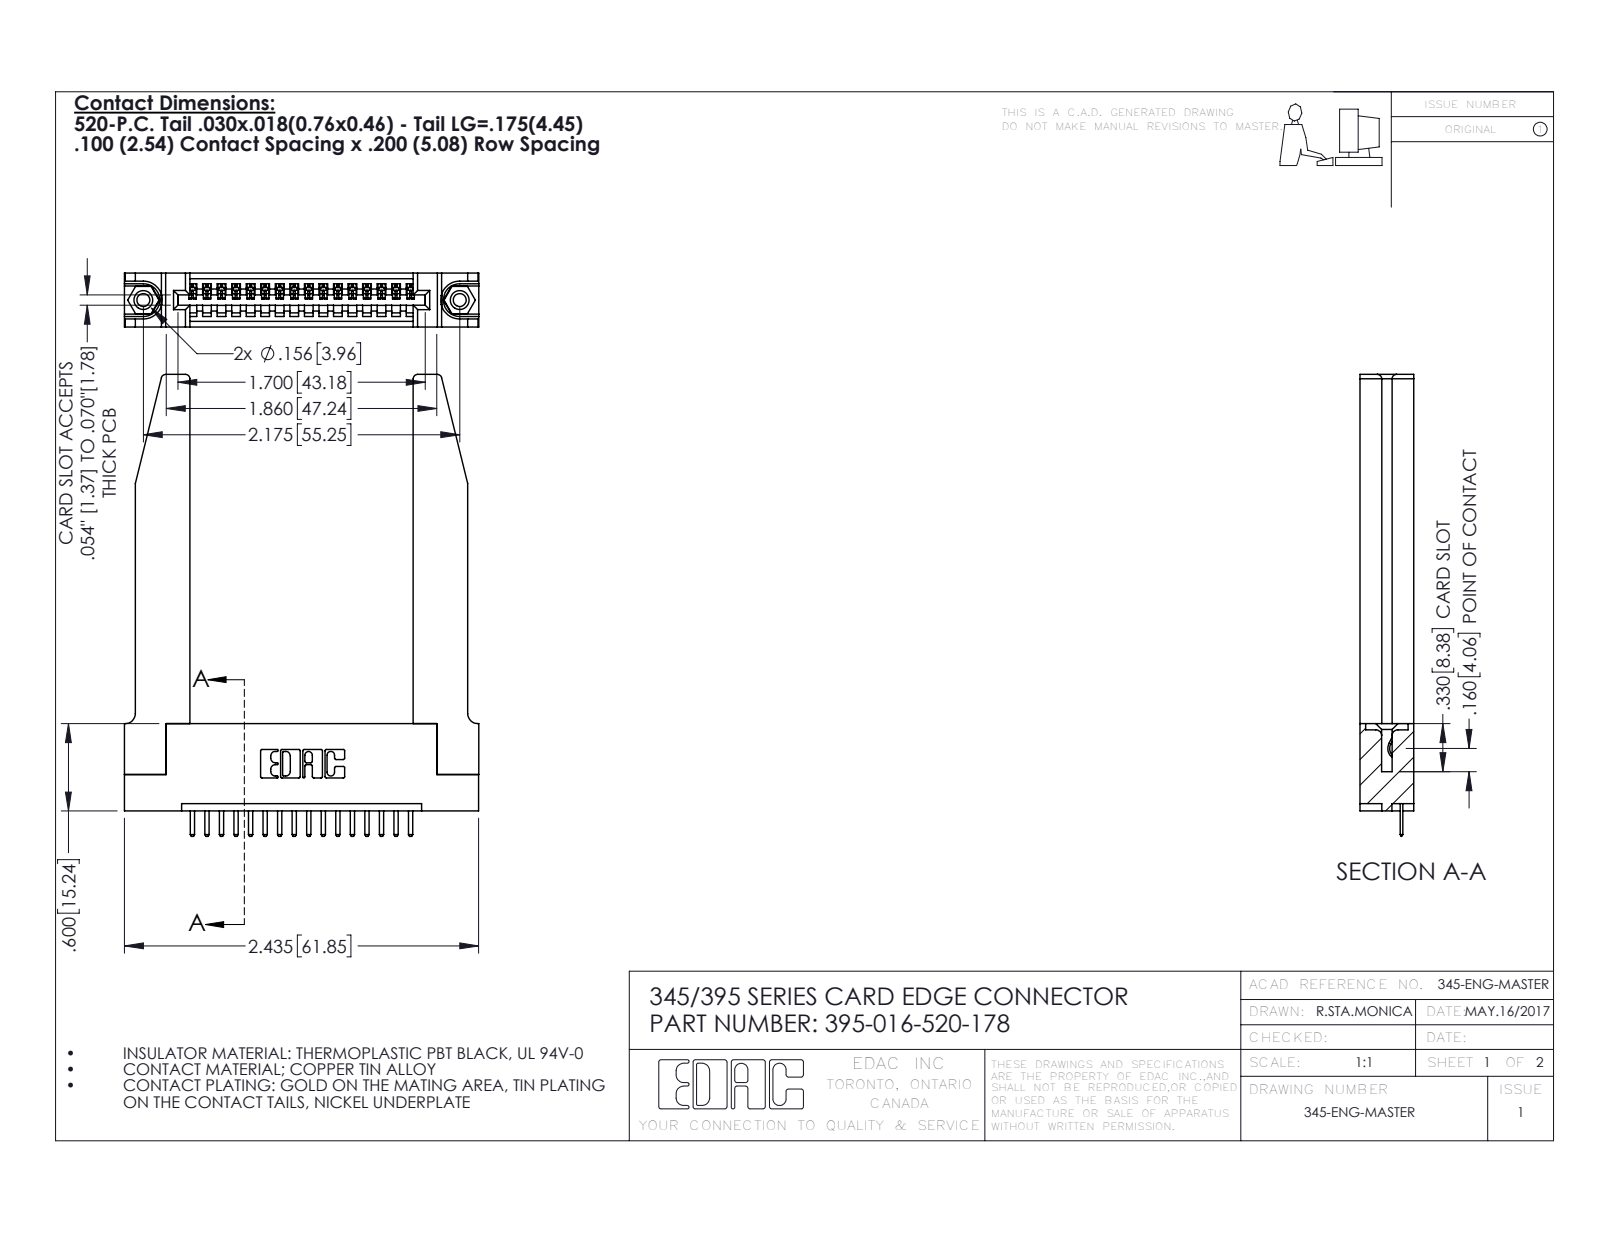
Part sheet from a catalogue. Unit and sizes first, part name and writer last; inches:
Units: inches
Overall size (bounding box): 3.175 × 2.436 × 0.37
Round holes (diameter × count): ⌀0.089 ×2, ⌀0.125 ×2, ⌀0.156 ×2, ⌀0.064 ×1
Round bosses / shafts (diameter × count): ⌀0.155 ×2
Partial cylindrical surfaces — rounded edges, fillets, slot ends (radius × count): R0.01 ×34, R0.006 ×32, R0.01 ×22, R0.03 ×8, R0.007 ×6, R0.031 ×6, R0.026 ×3, R0.031 ×2
Main face-to-face distances: 0.37, 0.072, 0.298, 0.2, 0.148, 0.15, 0.077, 0.22, 1.535, 0.098
Hole centre spacings: 0.27, 1.942, 2.175
Volume: 0.817 in³ · Surface area: 21.4 in²
Bodies: 21 solids, 1352 faces (894 planar, 406 cylindrical, 52 other)
Part name (STEP PRODUCT): 395-016-520-178; 345 Part_Flush Mounting Lugs - 0.156 Dia-TH; 345-220-078_345-220-078; 345-292-001_345-293-120 (+1 more)
STEP written by: SolidWorks 2016 (CONFIG_CONTROL_DESIGN)
